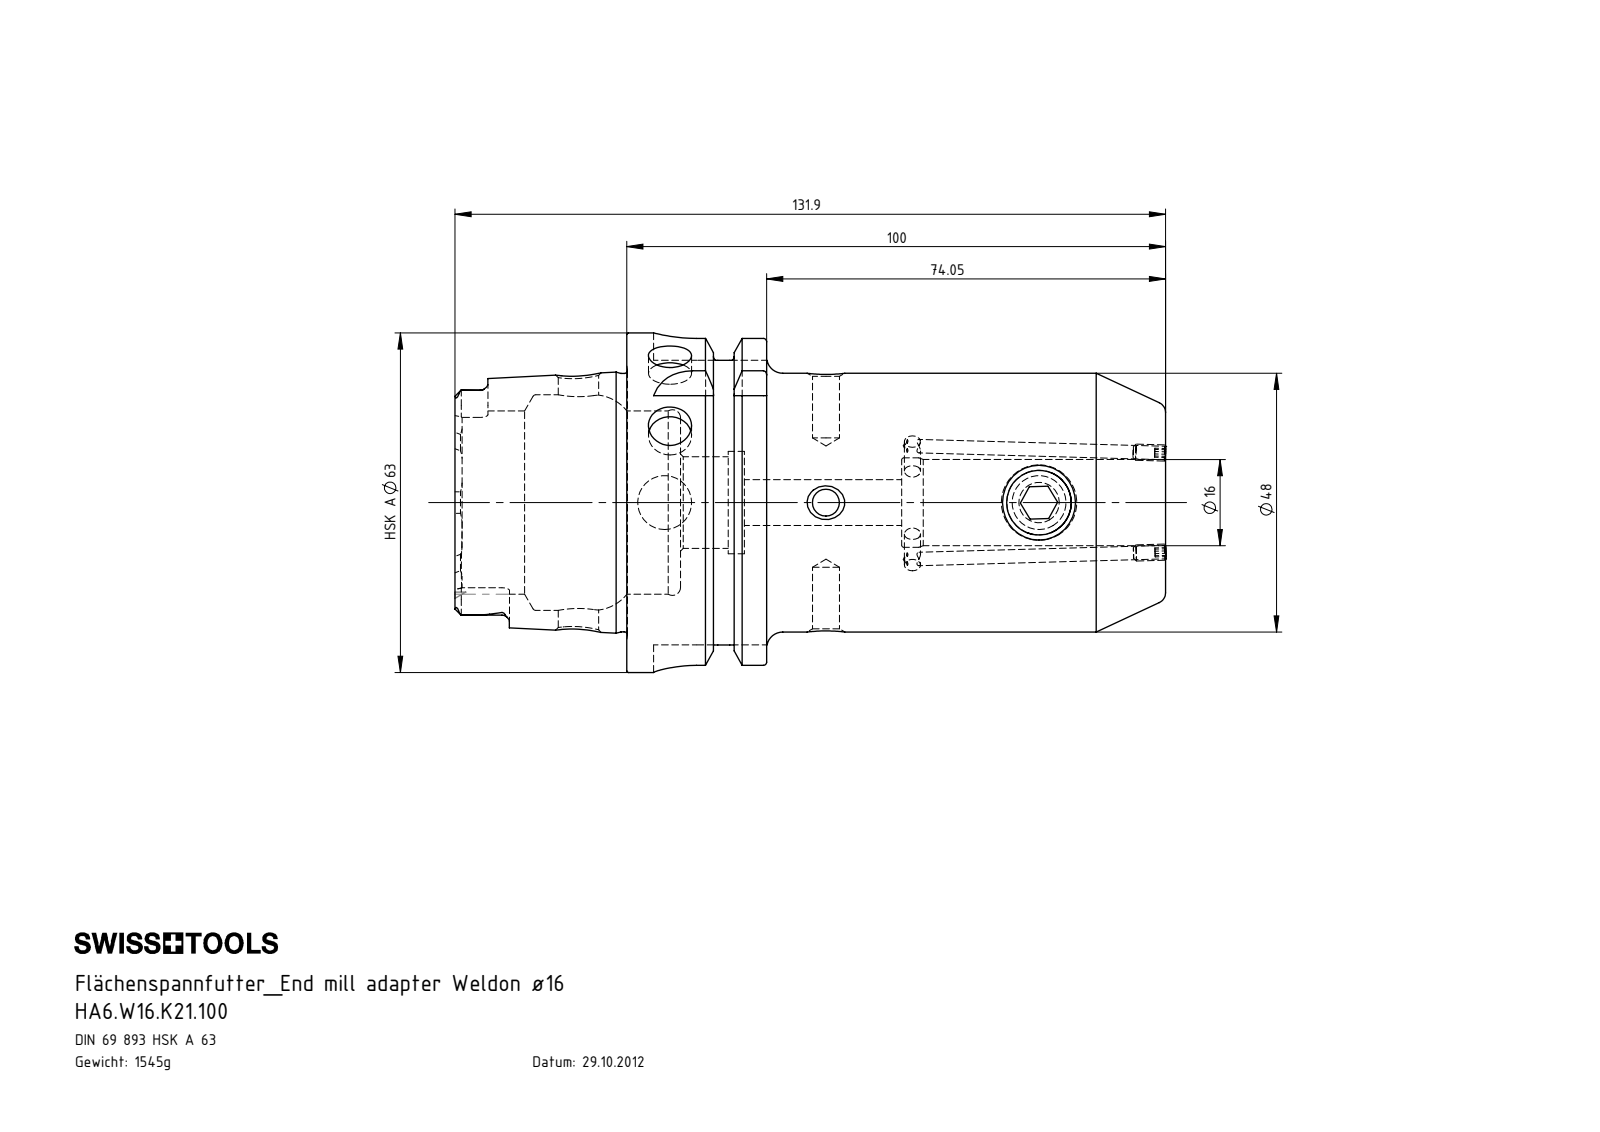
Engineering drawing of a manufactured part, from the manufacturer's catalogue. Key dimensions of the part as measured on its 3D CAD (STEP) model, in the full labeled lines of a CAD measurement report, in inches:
Part name (STEP PRODUCT): HA6-W16.K21.100; ERU-CJ2.001.006; W16-ER1.001.016; HA6-W16.K21.100_A_Fertigbearbeitung
STEP written by: SolidWorks 2012 (CONFIG_CONTROL_DESIGN)
Units: inches
Bodies: 4 solids, 287 faces (78 planar, 81 cylindrical, 128 other)
Overall size (bounding box): 5.196 × 2.48 × 2.48
Volume: 12.01 in³ · Surface area: 60.41 in²
Round holes (diameter × count): ⌀0.098 ×2, ⌀0.197 ×2, ⌀0.315 ×2, ⌀0.118 ×1, ⌀0.295 ×1, ⌀0.335 ×1, ⌀0.394 ×1, ⌀0.472 ×1, ⌀0.63 ×1, ⌀0.654 ×1, ⌀0.669 ×1, ⌀0.748 ×1
Round bosses / shafts (diameter × count): ⌀0.118 ×2, ⌀2.48 ×1, ⌀2.163 ×1, ⌀1.89 ×1, ⌀1.887 ×1, ⌀0.551 ×1
Partial cylindrical surfaces — rounded edges, fillets, slot ends (radius × count): R0.055 ×6, R0.113 ×4, R0.315 ×4
Main face-to-face distances: 3.937, 1.022, 2.915, 0.63, 0.392, 3.545, 1.256, 1.648, 2.278, 5.193
Hole centre spacings: 1.179, 1.557, 1.809, 2.736
